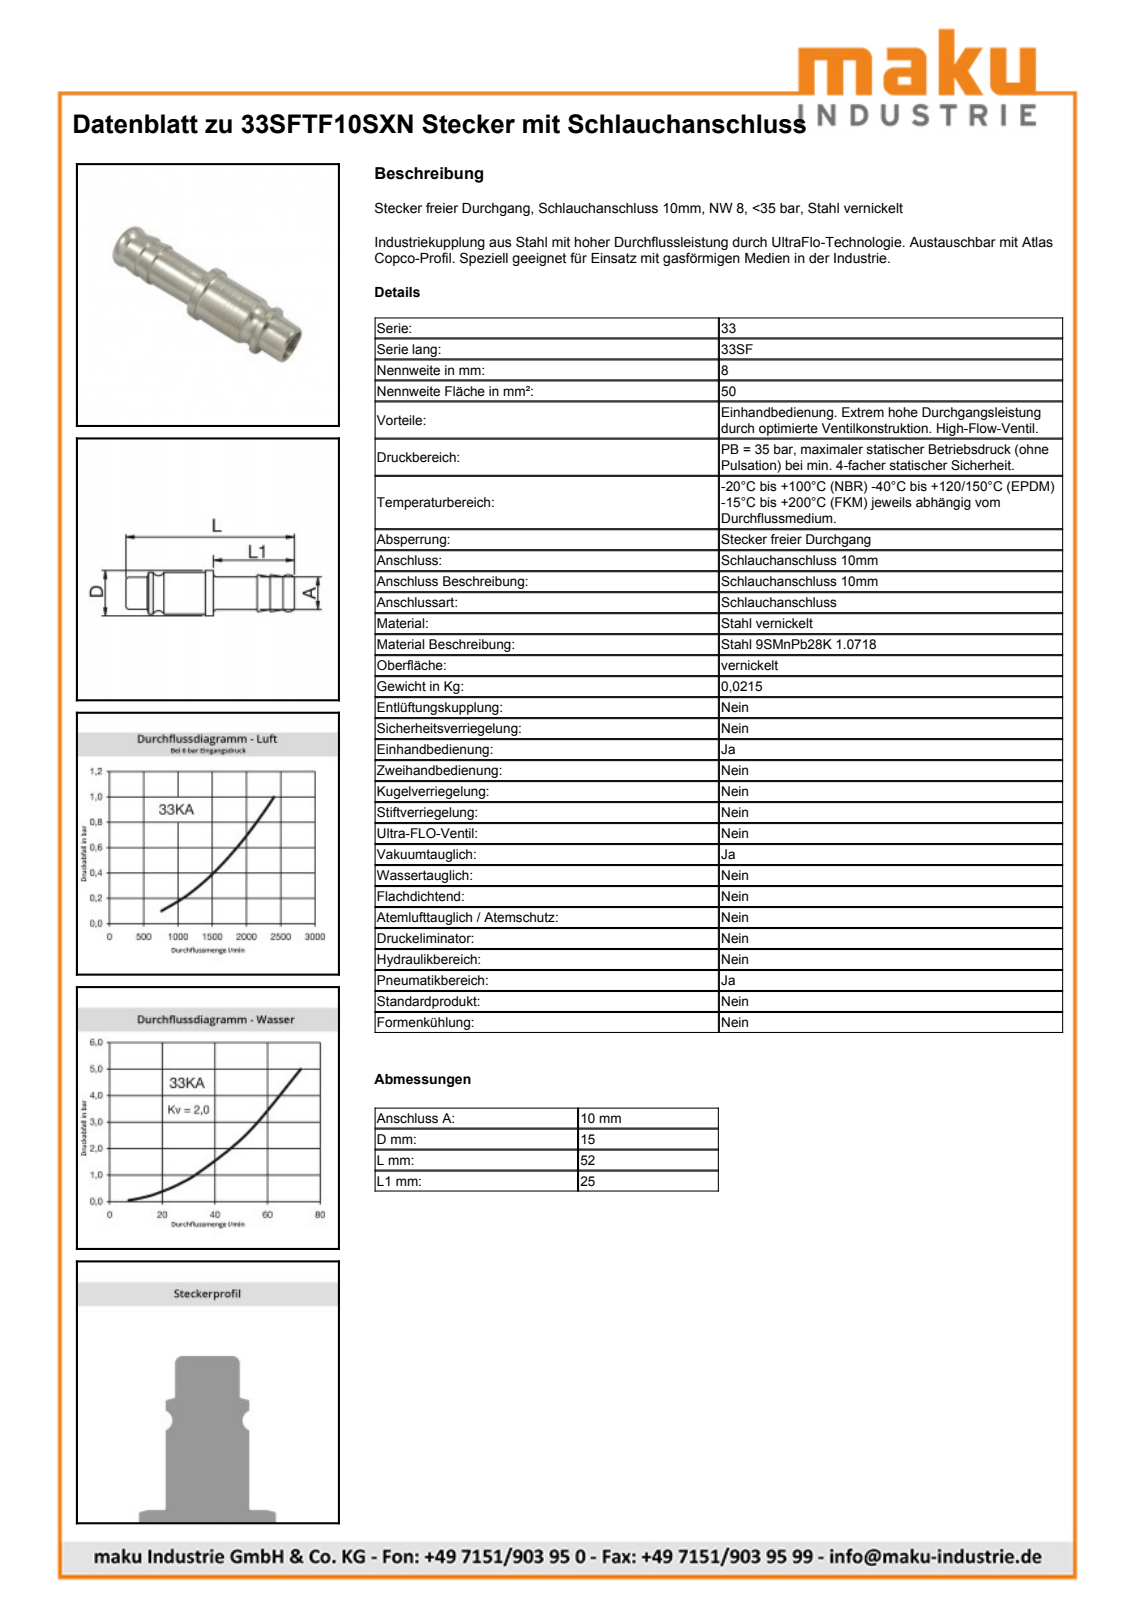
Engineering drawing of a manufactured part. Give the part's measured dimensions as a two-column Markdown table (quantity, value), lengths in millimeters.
| quantity | value |
| --- | --- |
| part name | D107394 |
| STEP written by | Autodesk Inventor 2013 (AUTOMOTIVE_DESIGN) |
| units | millimeters |
| bodies | 1 solid, 23 faces (6 planar, 6 cylindrical, 11 other) |
| overall size | 52 × 14 × 14 |
| volume | 2 791 mm³ |
| surface area | 3 354 mm² |
| round holes (diameter × count) | 7.8 × 1 |
| round bosses / shafts (diameter × count) | 14 × 1, 12.9 × 1, 10.1 × 1, 9.9 × 1 |
| main face-to-face distances | 25, 13.5, 11.5, 2.5, 16, 27.5, 20, 17.5, 4, 7.5 |
